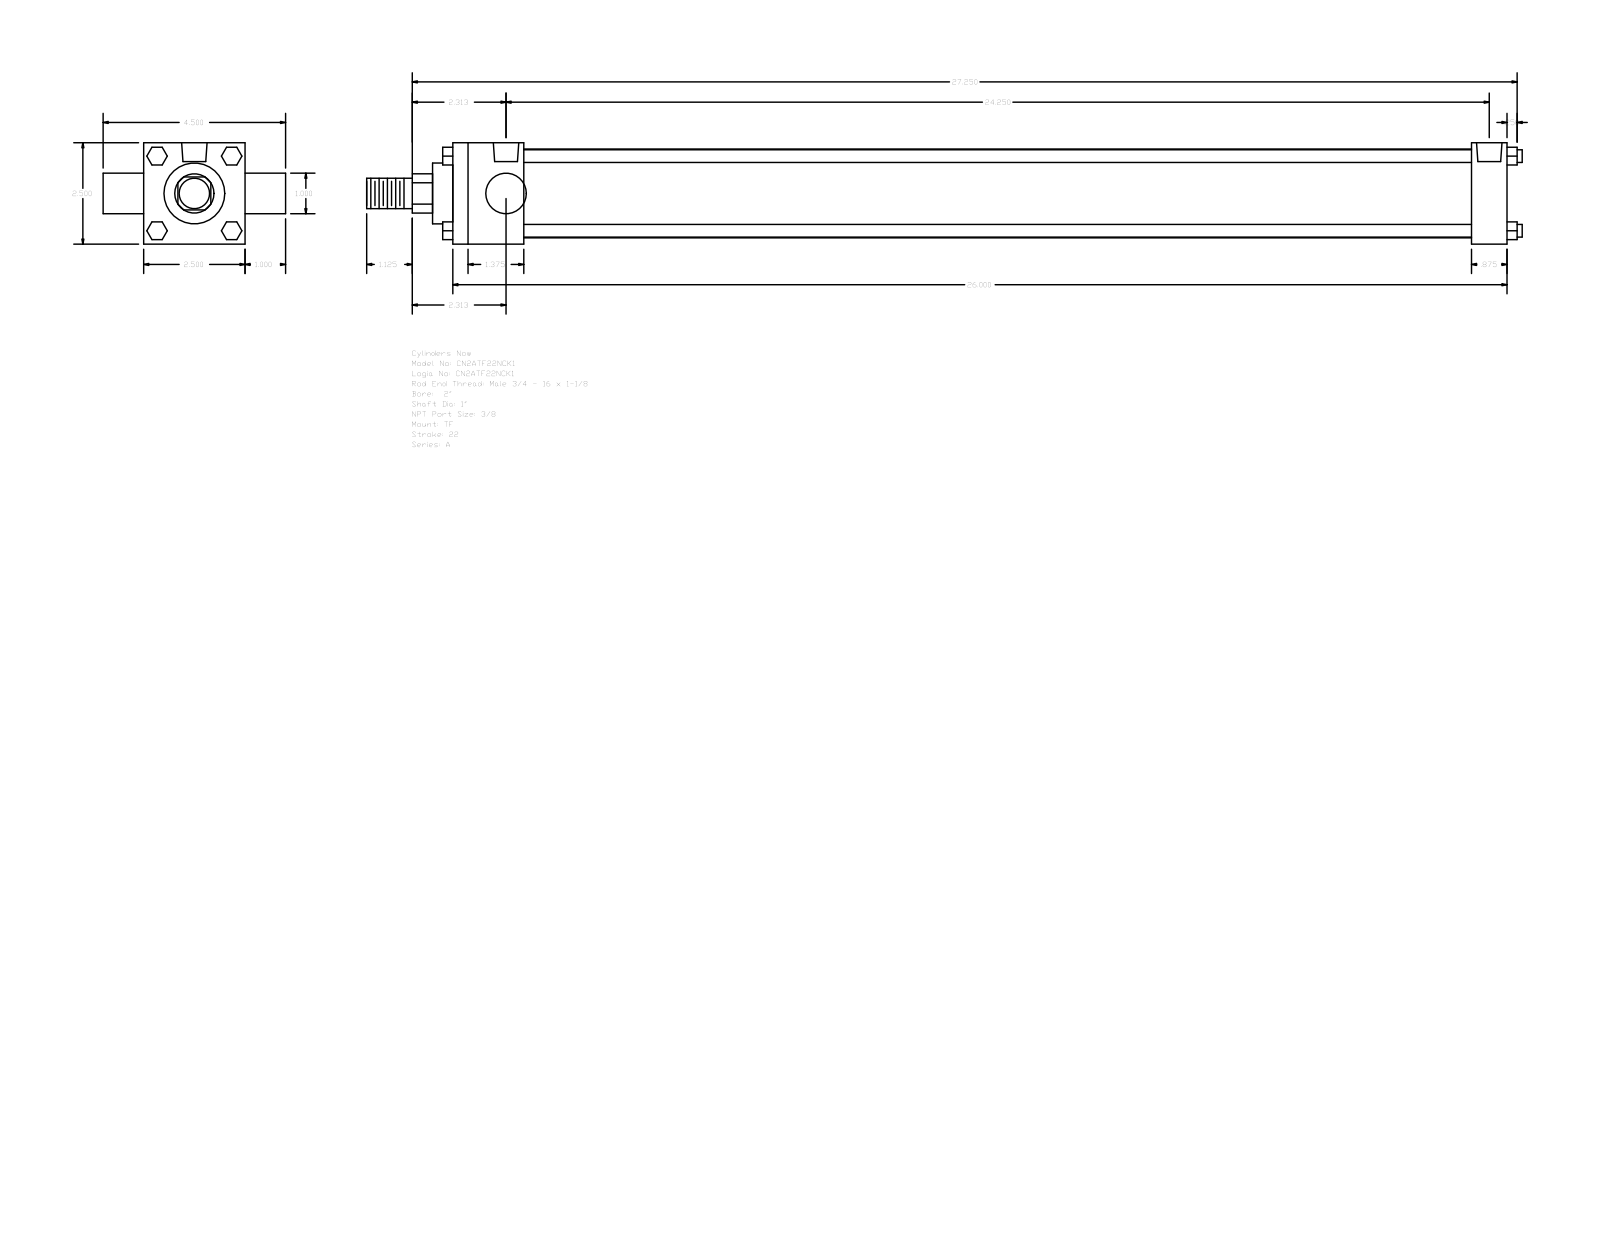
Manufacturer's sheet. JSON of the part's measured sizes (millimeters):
{"part_name": "A_TF__0200_1", "step_written_by": "GSSL Pune (CONFIG_CONTROL_DESIGN)", "units": "millimeters", "bodies": {"solids": 0, "faces": 120, "planar": 92, "cylindrical": 28, "other": 0}, "overall_size": [723.9, 114.3, 63.5], "round_holes": [[5.56, 3], [15.93, 2]], "round_bosses_or_shafts": [[7.94, 4], [25.4, 2], [55.63, 1], [38.1, 1], [19.05, 1]], "partial_cylinders_radius": [[12.29, 1]], "face_to_face_distances": [63.5, 660.4, 44.45, 638.18, 593.73, 615.95, 22.22, 25.4, 88.9, 673.1], "hole_center_spacings": [1.59, 3.98, 610.38, 611.97, 614.36, 615.95]}
